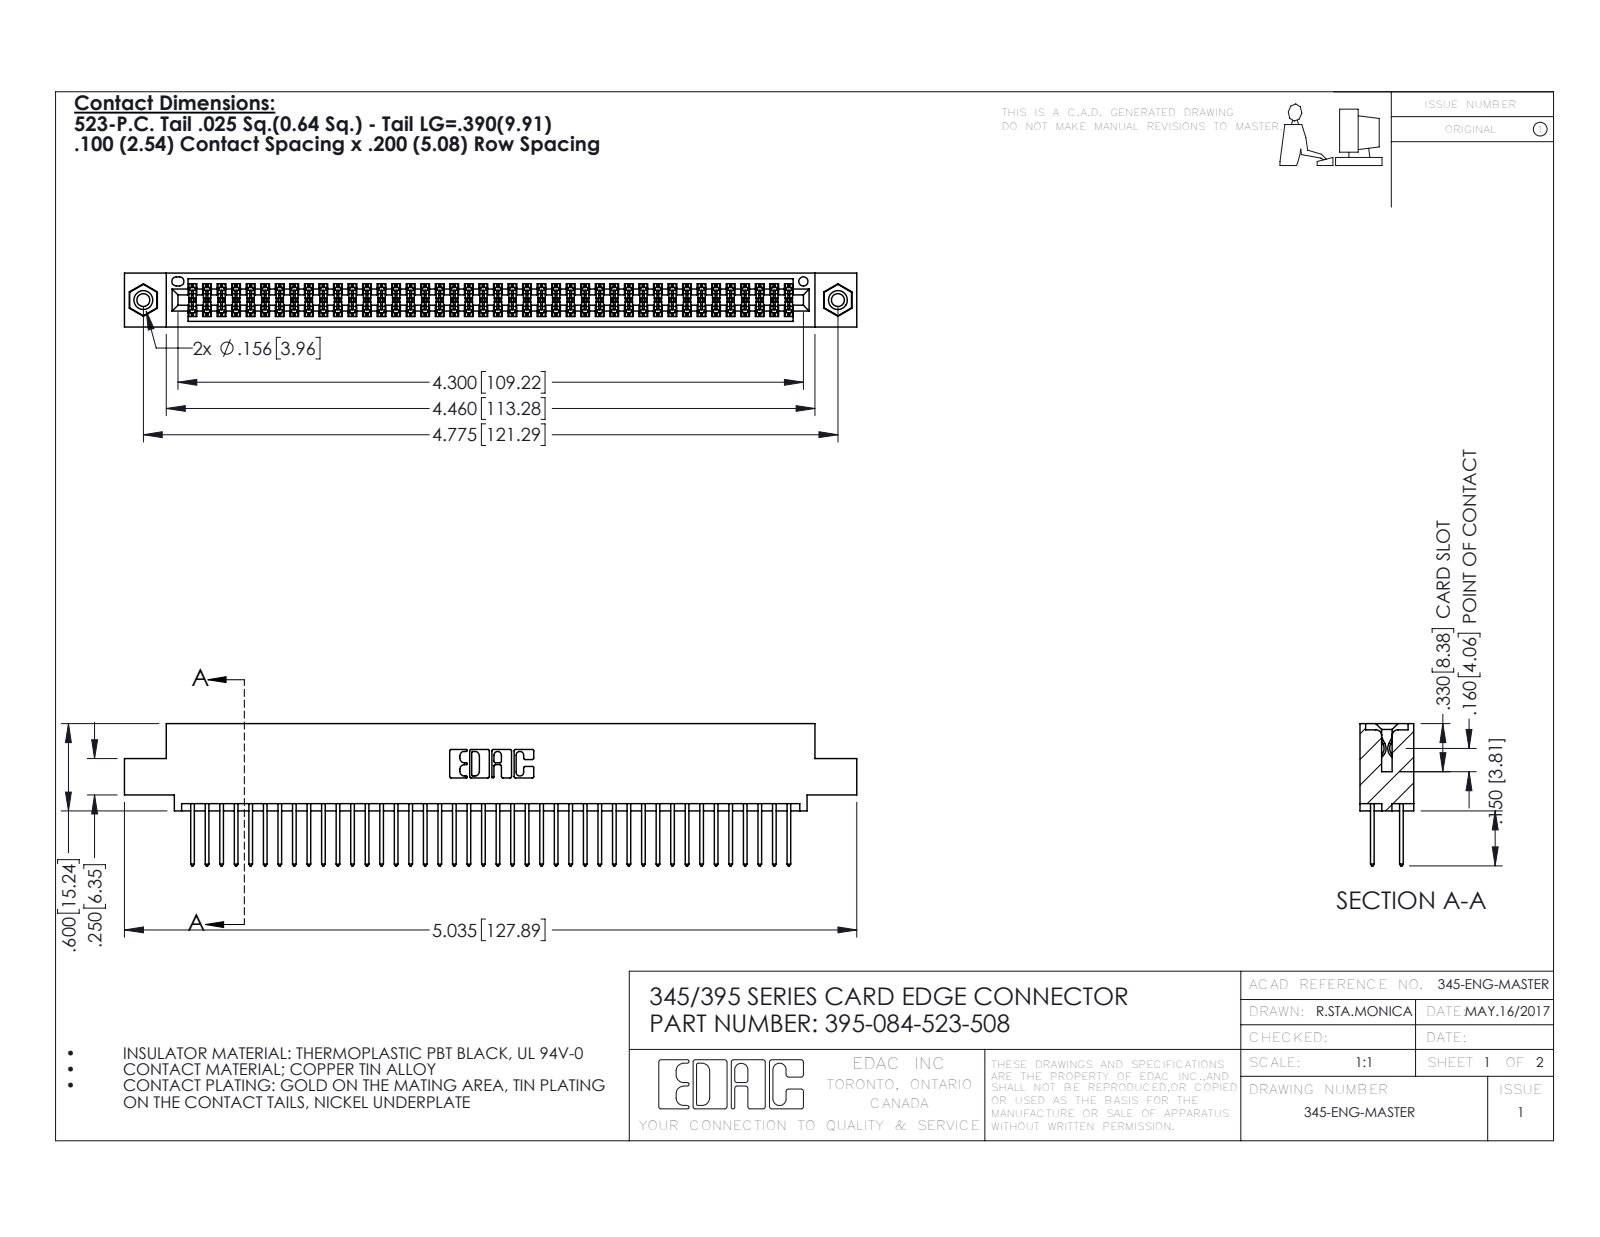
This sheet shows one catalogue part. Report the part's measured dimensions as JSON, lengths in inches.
{"part_name": "345-250-001_345-250-003-102; 395-084-523-508; 345-292-001_345-293-123; 345 Part_0.110 Offset - 0.156 Dia-TI", "step_written_by": "SolidWorks 2016 (CONFIG_CONTROL_DESIGN)", "units": "inches", "bodies": {"solids": 87, "faces": 4390, "planar": 2888, "cylindrical": 1486, "other": 16}, "overall_size": [5.035, 0.977, 0.37], "volume_in3": 0.764, "surface_area_in2": 30.04, "round_holes": [[0.089, 2], [0.125, 2], [0.156, 2], [0.064, 1]], "round_bosses_or_shafts": [[0.155, 2]], "partial_cylinders_radius": [[0.006, 126], [0.01, 84], [0.01, 22], [0.007, 6], [0.031, 6], [0.026, 3], [0.014, 2], [0.019, 2]], "face_to_face_distances": [0.072, 0.298, 0.2, 0.098, 0.272, 0.025, 0.37, 0.225, 0.175, 0.149], "hole_center_spacings": [0.27, 4.539, 4.775]}
